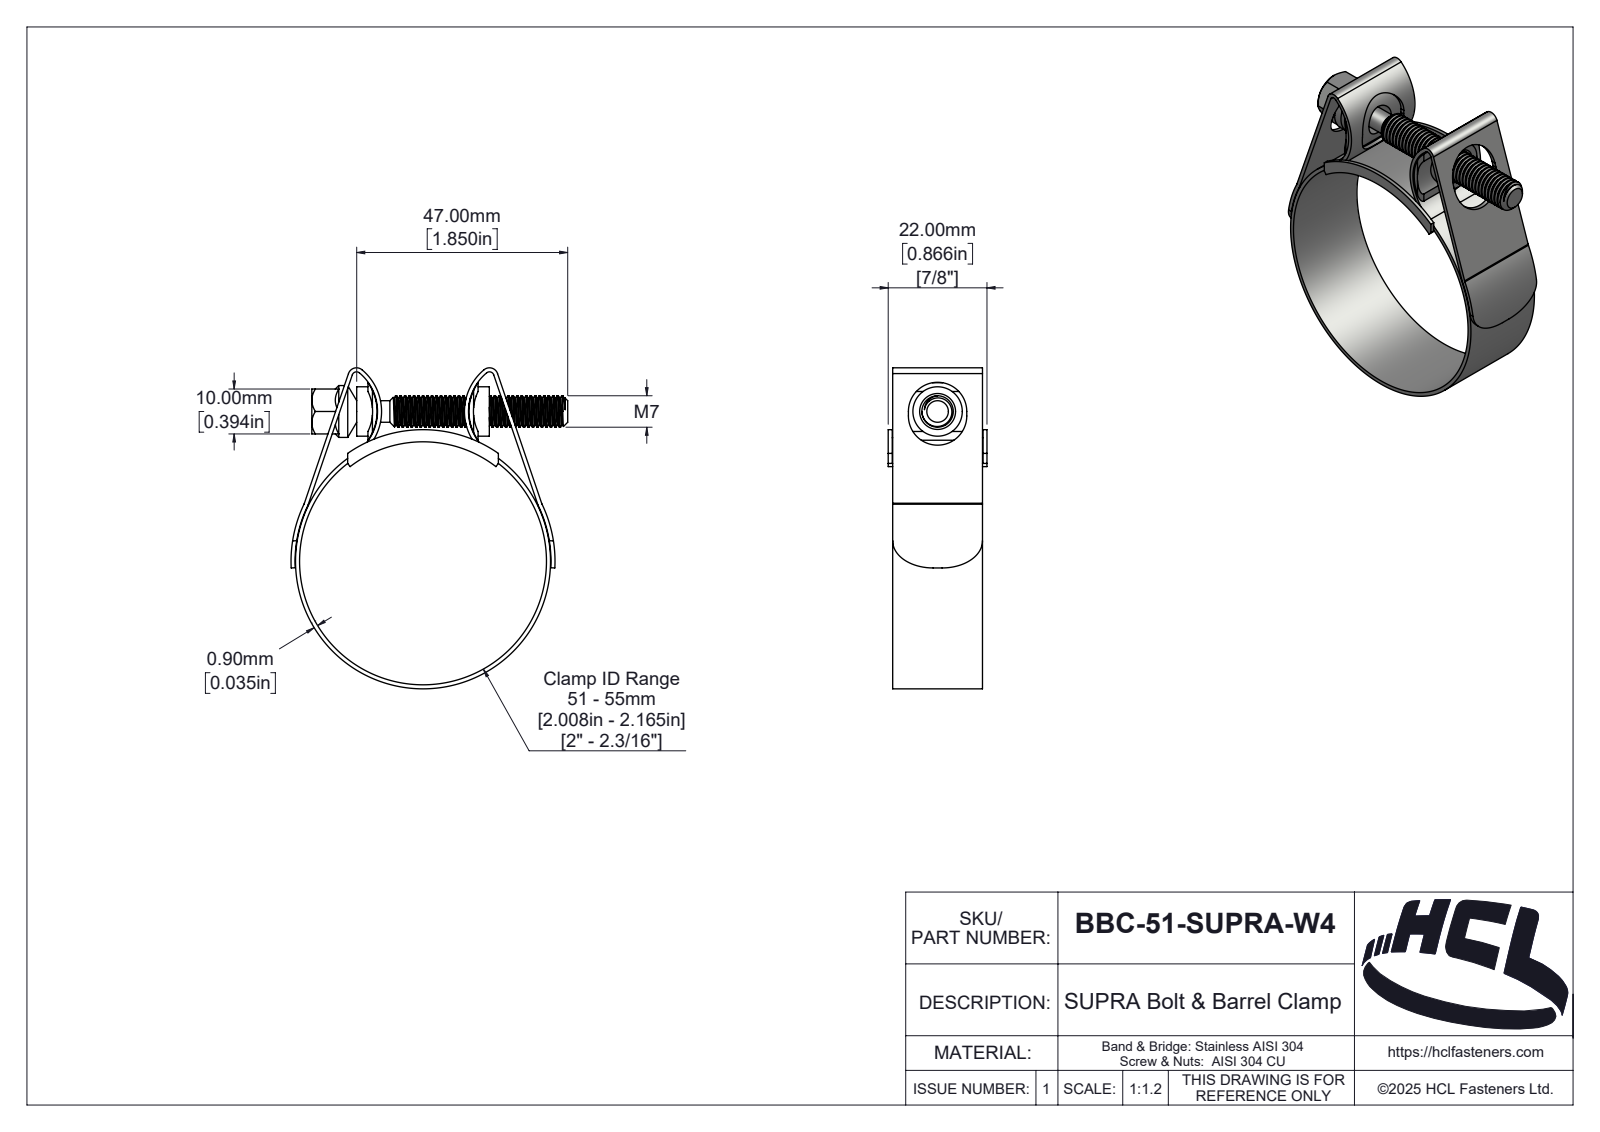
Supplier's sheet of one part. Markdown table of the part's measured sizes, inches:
| quantity | value |
| --- | --- |
| part name | BBC-51-SUPRA-W4 |
| STEP written by | SolidWorks 2025 (AUTOMOTIVE_DESIGN) |
| units | inches |
| bodies | 5 solids, 319 faces (46 planar, 193 cylindrical, 80 other) |
| overall size | 2.814 × 2.426 × 0.866 |
| volume | 0.508 in³ |
| surface area | 24.57 in² |
| round holes (diameter × count) | 2.165 × 1 |
| round bosses / shafts (diameter × count) | 2.236 × 1, 0.455 × 1, 0.433 × 1, 0.276 × 1, 0.189 × 1 |
| partial cylindrical surfaces (radius × count) | 0.039 × 6, 0.075 × 2, 0.079 × 2, 0.114 × 2, 0.256 × 2, 0.396 × 2, 0.436 × 2, 0.44 × 2 |
| main face-to-face distances | 0.035, 0.787, 0.039, 0.827, 0.394, 0.831, 0.791, 0.866, 0.098, 1.065 |
